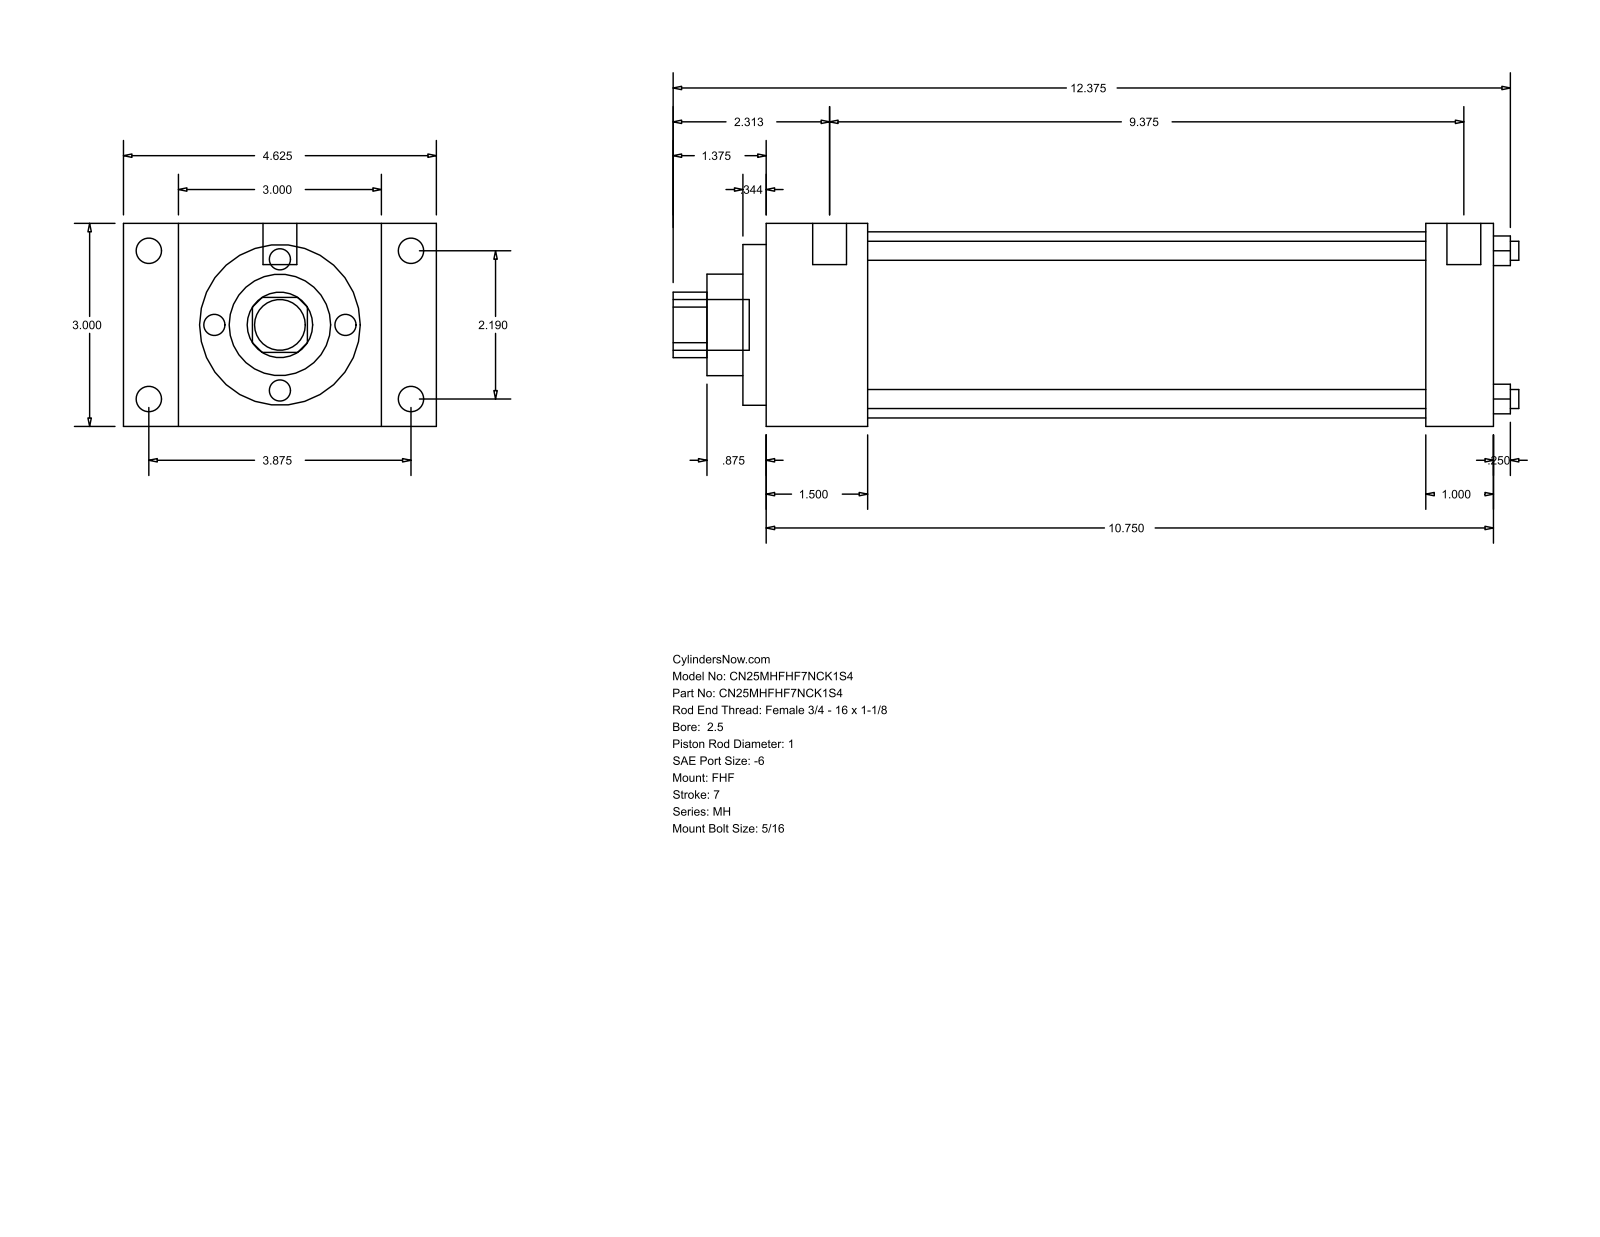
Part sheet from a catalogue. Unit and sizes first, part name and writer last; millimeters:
Units: millimetres
Overall size (bounding box): 317.5 × 117.47 × 76.2
Round holes (diameter × count): ⌀7.14 ×4, ⌀25.4 ×1, ⌀38.1 ×1, ⌀60.33 ×1, ⌀69.85 ×1
Round bosses / shafts (diameter × count): ⌀9.53 ×4, ⌀5.56 ×4, ⌀12.7 ×2, ⌀19.05 ×1
Partial cylindrical surfaces — rounded edges, fillets, slot ends (radius × count): R12.29 ×1
Main face-to-face distances: 76.2, 273.06, 38.11, 234.95, 20.64, 96.84, 117.48, 247.65, 209.54, 25.41
Hole centre spacings: 39.33, 55.62, 78.66
Bodies: 0 solids, 90 faces (61 planar, 29 cylindrical, 0 other)
Part name (STEP PRODUCT): MH_FHF__0250_1
STEP written by: GSSL Pune (CONFIG_CONTROL_DESIGN)
